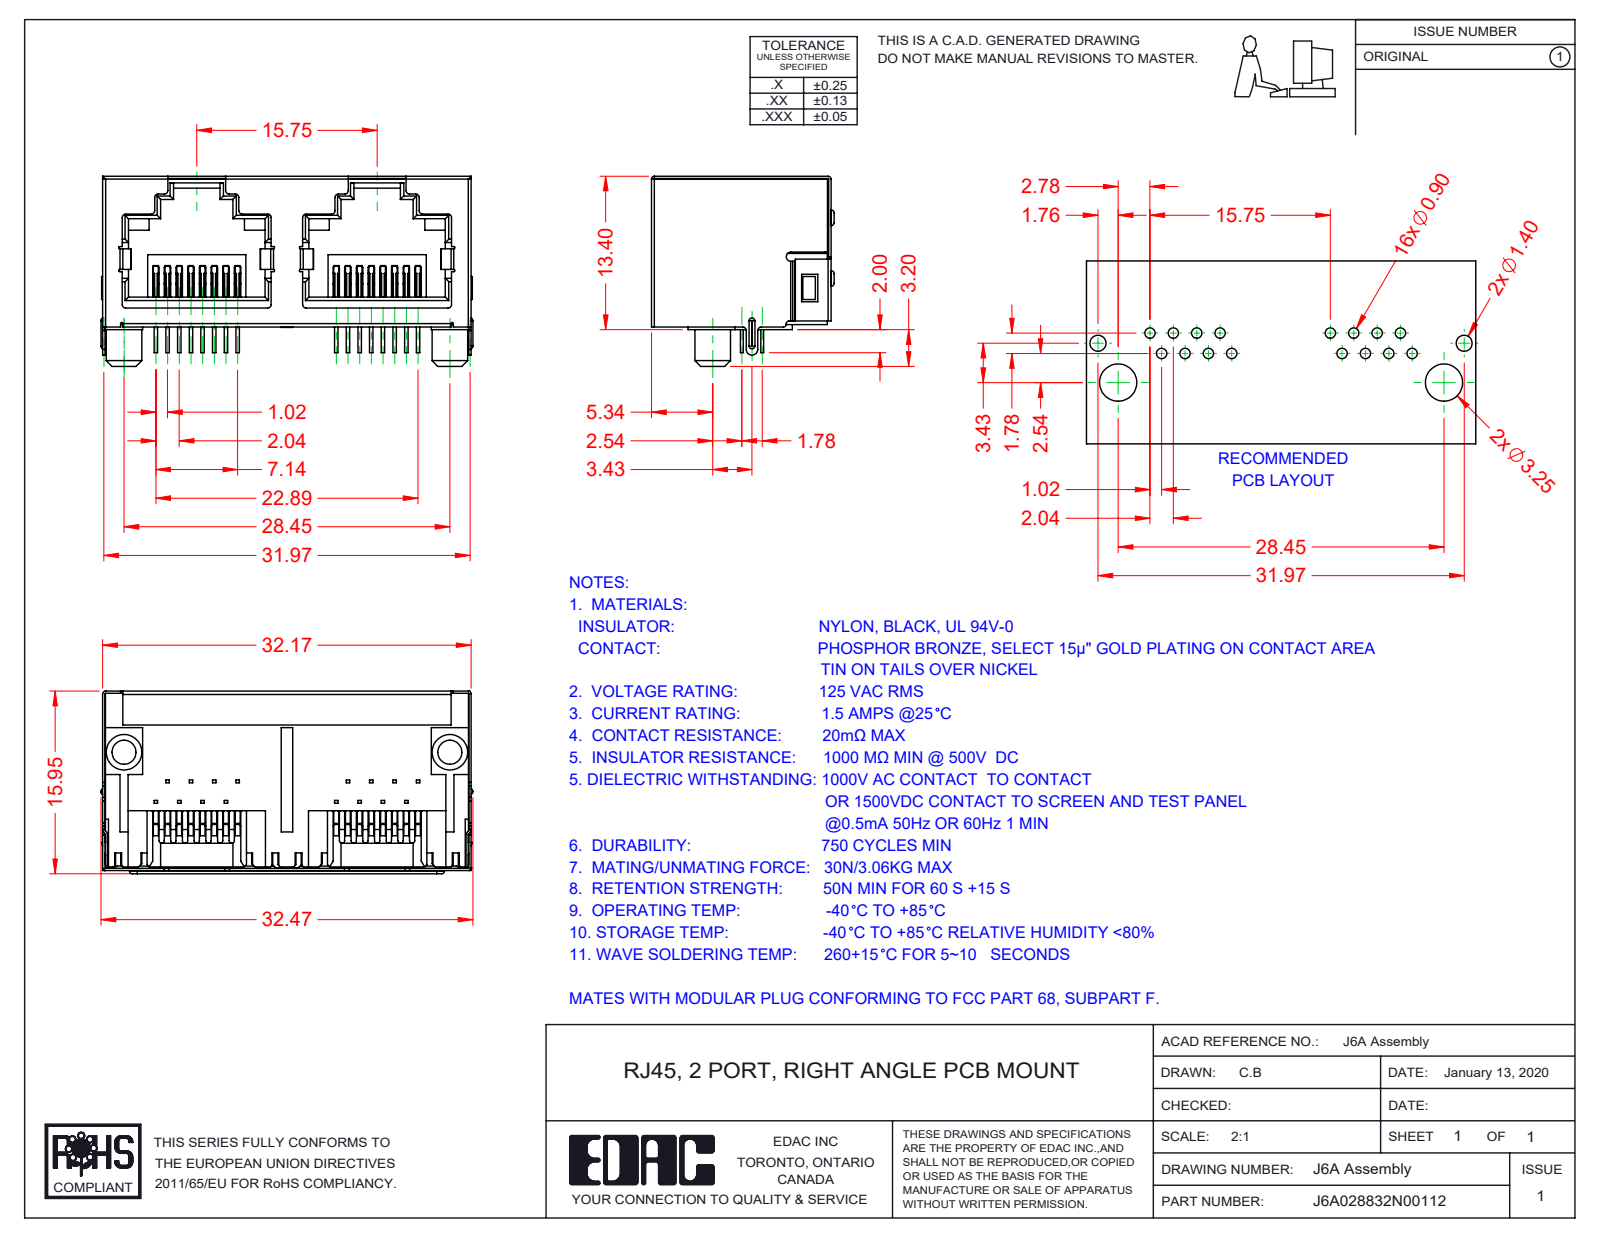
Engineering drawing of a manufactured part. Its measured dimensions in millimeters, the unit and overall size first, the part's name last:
Units: millimetres
Overall size (bounding box): 32.47 × 16.6 × 15.95
Round bosses / shafts (diameter × count): ⌀3.1 ×2
Partial cylindrical surfaces — rounded edges, fillets, slot ends (radius × count): R0.1 ×44, R0.3 ×44, R0.25 ×23, R0.2 ×16, R0.23 ×14, R0.21 ×4, R0.47 ×4, R0.68 ×4
Main face-to-face distances: 15.75, 0.85, 31.97, 12.95, 12.7, 12.75, 15.47, 10.55, 2, 2.4
Volume: 2 964 mm³ · Surface area: 8 172 mm²
Bodies: 18 solids, 1823 faces (1380 planar, 415 cylindrical, 28 other)
Part name (STEP PRODUCT): J6A028832N00112; 6A Shield; 6A Contacts; 6A Insulator
STEP written by: SolidWorks 2016 (CONFIG_CONTROL_DESIGN)
